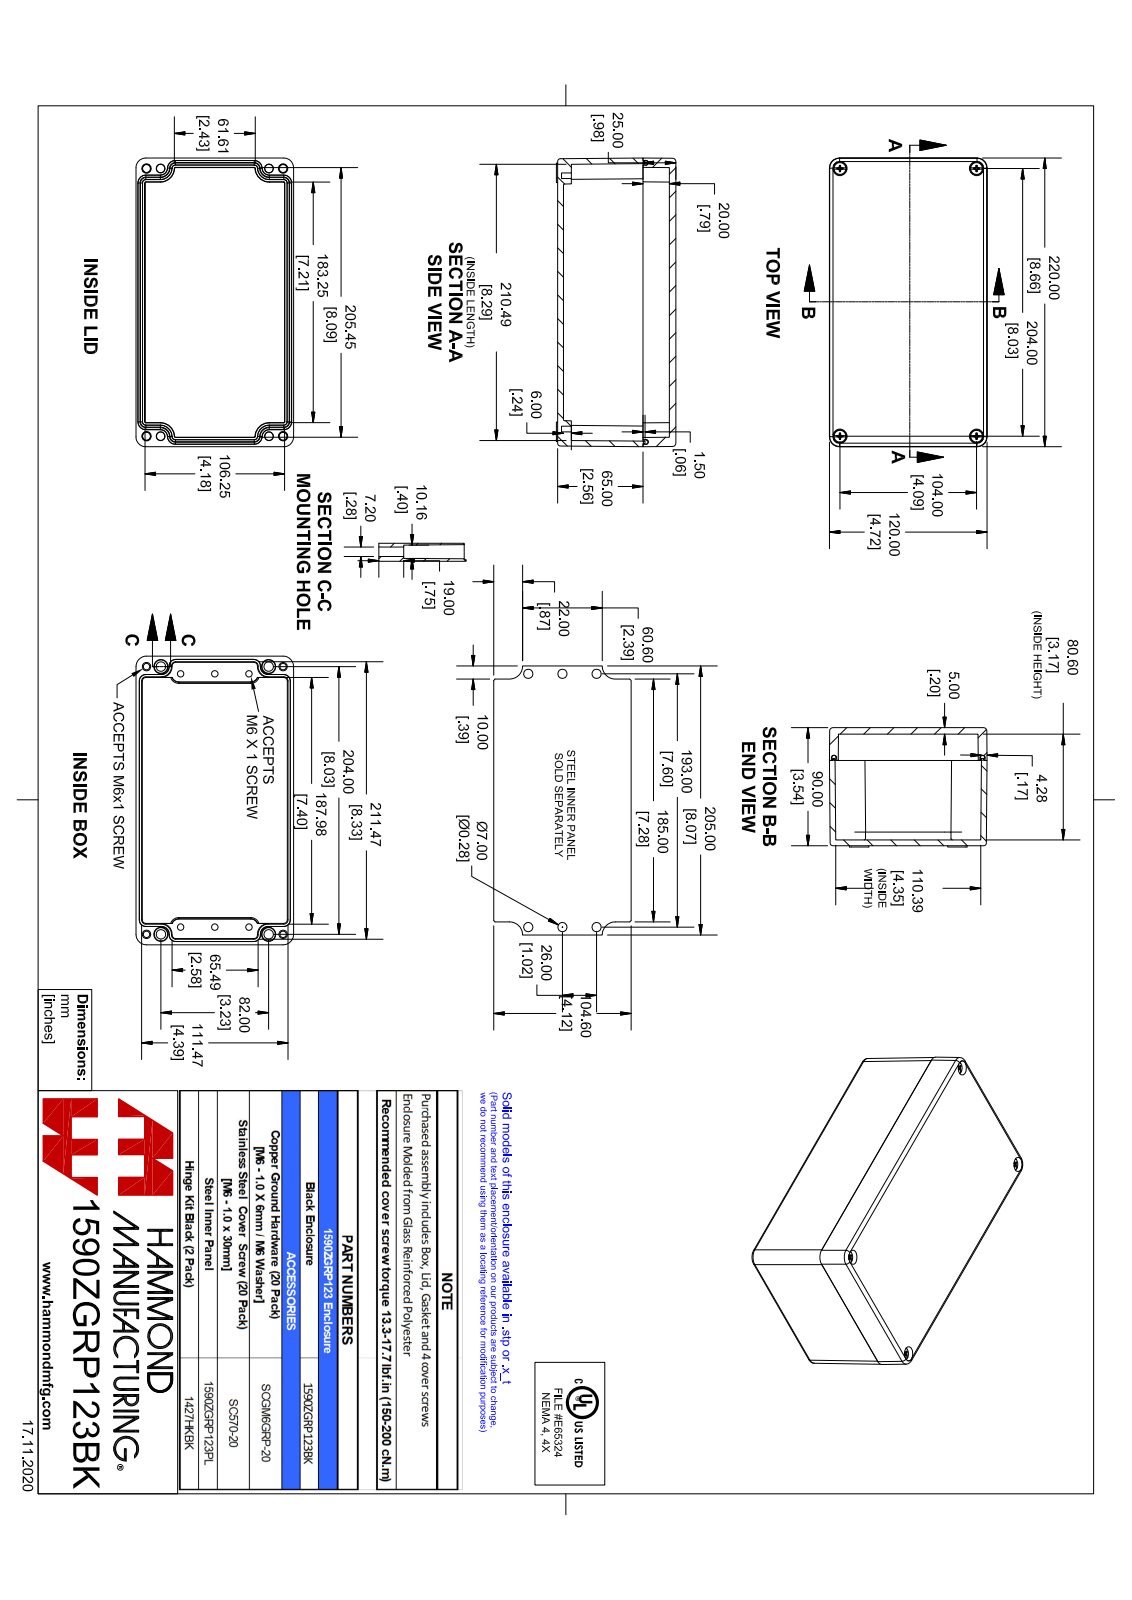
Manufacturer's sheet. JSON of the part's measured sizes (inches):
{"part_name": "1590ZGRP123BK", "step_written_by": "SolidWorks 2021 (AUTOMOTIVE_DESIGN)", "units": "inches", "bodies": {"solids": 7, "faces": 455, "planar": 219, "cylindrical": 84, "other": 152}, "overall_size": [8.661, 4.724, 3.583], "volume_in3": 34.64, "surface_area_in2": 374.7, "round_holes": [[0.194, 10], [0.236, 4], [0.252, 4], [0.283, 4], [0.425, 4]], "round_bosses_or_shafts": [[0.148, 6], [0.231, 4], [0.208, 4]], "partial_cylinders_radius": [[0.059, 20], [0.079, 4], [0.098, 4], [0.295, 4], [0.315, 4], [0.039, 2]], "face_to_face_distances": [0.169, 3.543, 3.346, 0.197, 0.173, 3.173, 3.37, 4.556, 4.724, 0.264], "hole_center_spacings": [0.433, 0.629, 1.024, 1.046, 1.629, 2.059, 2.647, 3.078]}
